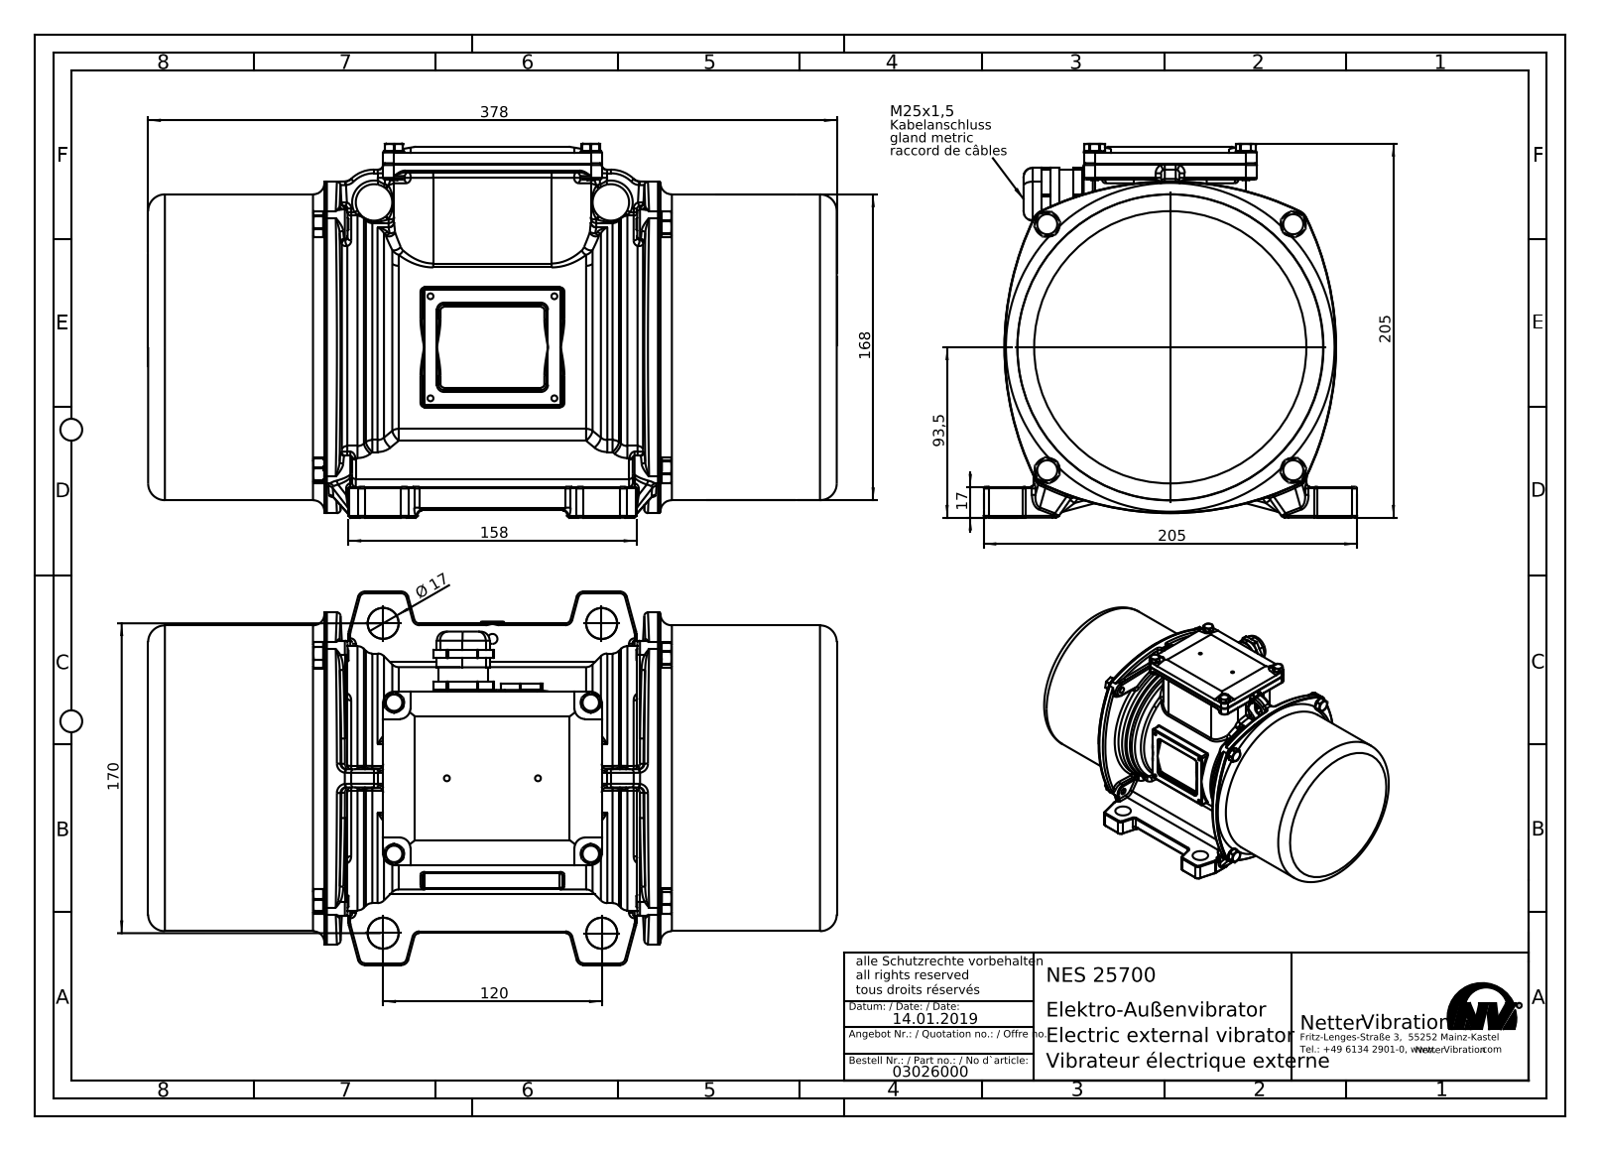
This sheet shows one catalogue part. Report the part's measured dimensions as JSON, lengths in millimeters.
{"part_name": "NES 25700 #03026000", "step_written_by": "SolidWorks 2015 (AUTOMOTIVE_DESIGN)", "units": "millimeters", "bodies": {"solids": 30, "faces": 3585, "planar": 1492, "cylindrical": 0, "other": 2093}, "overall_size": [378, 205.2, 205], "volume_mm3": 2617000, "surface_area_mm2": 671195, "face_to_face_distances": [1.2, 376.8, 89, 289, 87.8, 287.8, 9, 96.8, 280, 375.6]}
